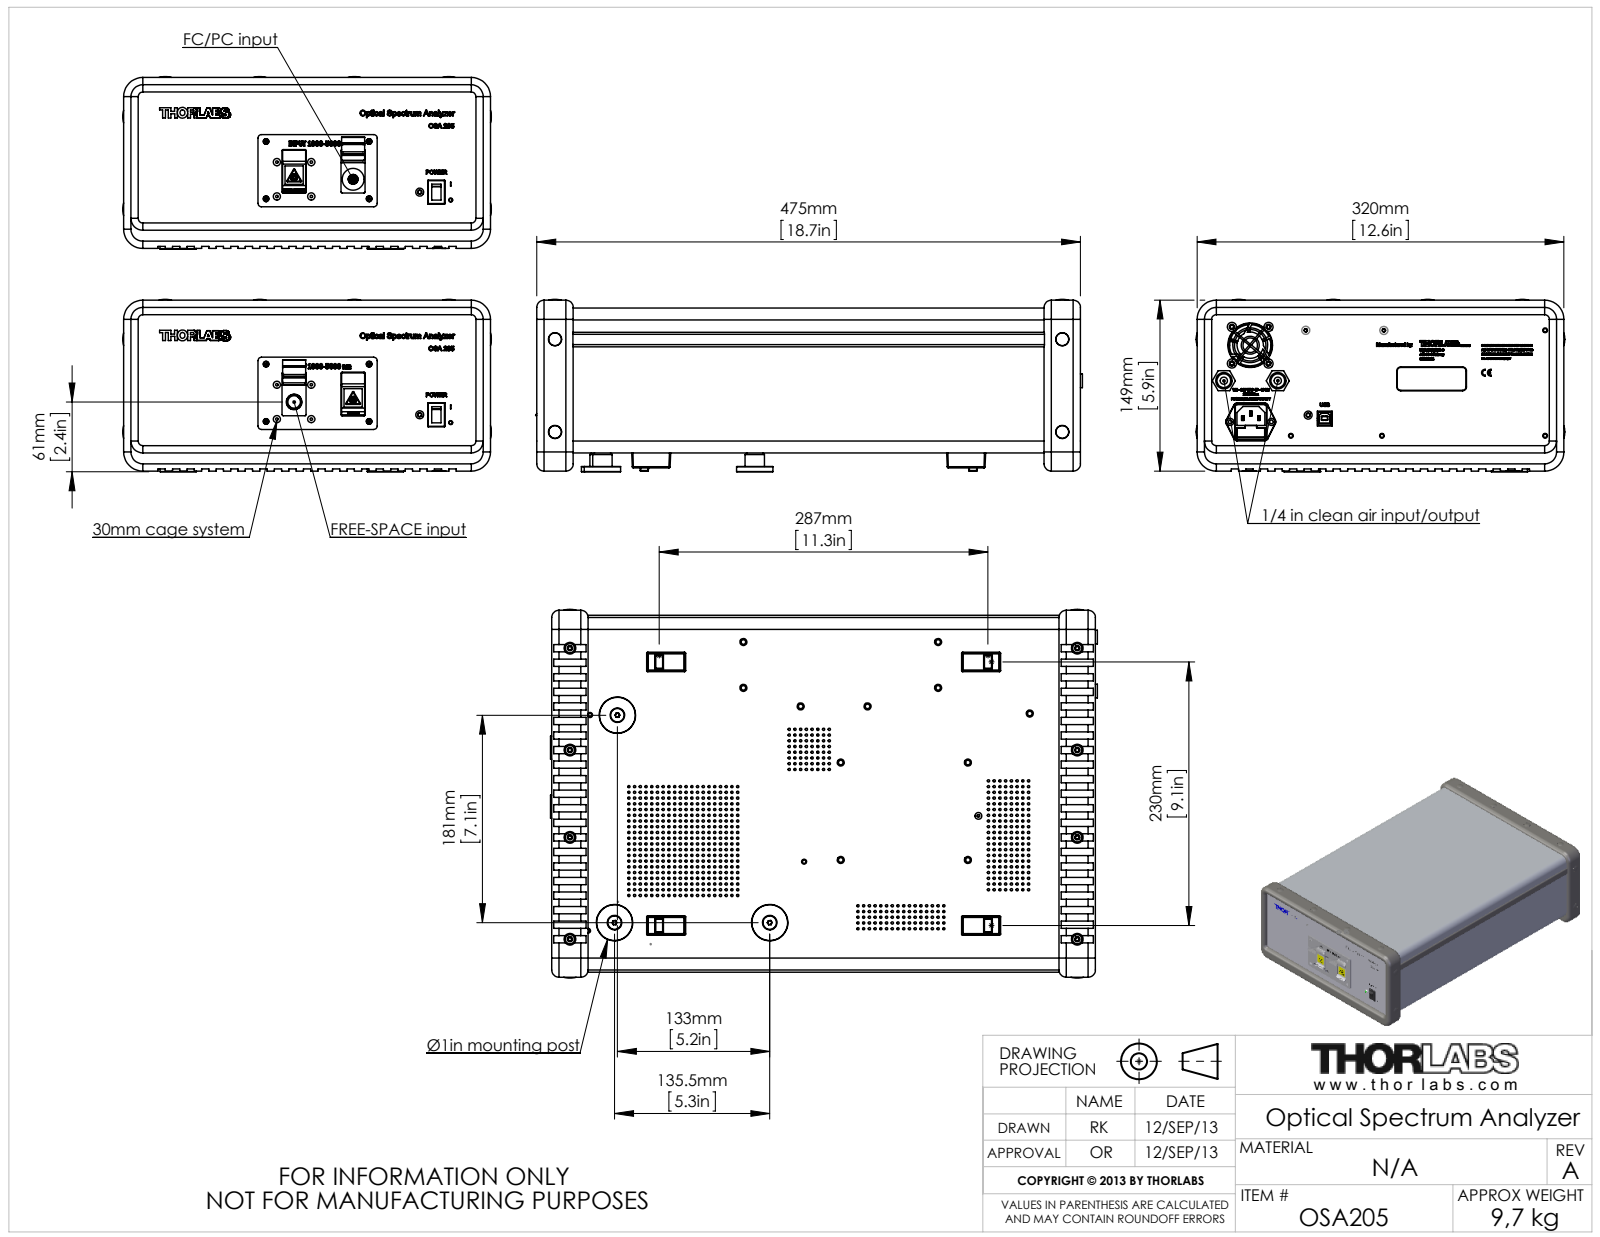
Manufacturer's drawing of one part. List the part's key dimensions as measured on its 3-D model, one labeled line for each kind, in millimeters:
Part name (STEP PRODUCT): STN012155-E0W with hiphen; Rexroth R432000156; Stöd free space; BE1_M (+8 more)
STEP written by: SolidWorks 2012 (AUTOMOTIVE_DESIGN)
Units: millimetres
Bodies: 486 solids, 29881 faces (13033 planar, 8288 cylindrical, 8560 other)
Overall size (bounding box): 496.54 × 321.82 × 150.61
Volume: 2 421 000 mm³ · Surface area: 1 891 000 mm²
Round holes (diameter × count): ⌀2 ×704, ⌀0.3 ×293, ⌀1 ×55, ⌀2.5 ×34, ⌀2.05 ×31, ⌀3.3 ×30, ⌀1.02 ×29, ⌀0.81 ×18, ⌀3.2 ×17, ⌀0.33 ×16, ⌀1.78 ×14, ⌀4.3 ×14
Round bosses / shafts (diameter × count): ⌀4 ×31, ⌀3 ×22, ⌀6.35 ×16, ⌀5 ×14, ⌀8 ×13, ⌀2.5 ×13, ⌀11.05 ×12, ⌀2.4 ×12
Partial cylindrical surfaces — rounded edges, fillets, slot ends (radius × count): R0.1 ×271, R0.27 ×72, R0.91 ×72, R0.5 ×63, R0.79 ×48, R1 ×38, R3 ×38, R1.5 ×31
Main face-to-face distances: 1, 125.4, 124.4, 126.4, 306.6, 461, 90.65, 34.75, 307.6, 15
Hole centre spacings: 11.18, 5, 15.81, 7.07, 10, 18.03, 15, 20.62
